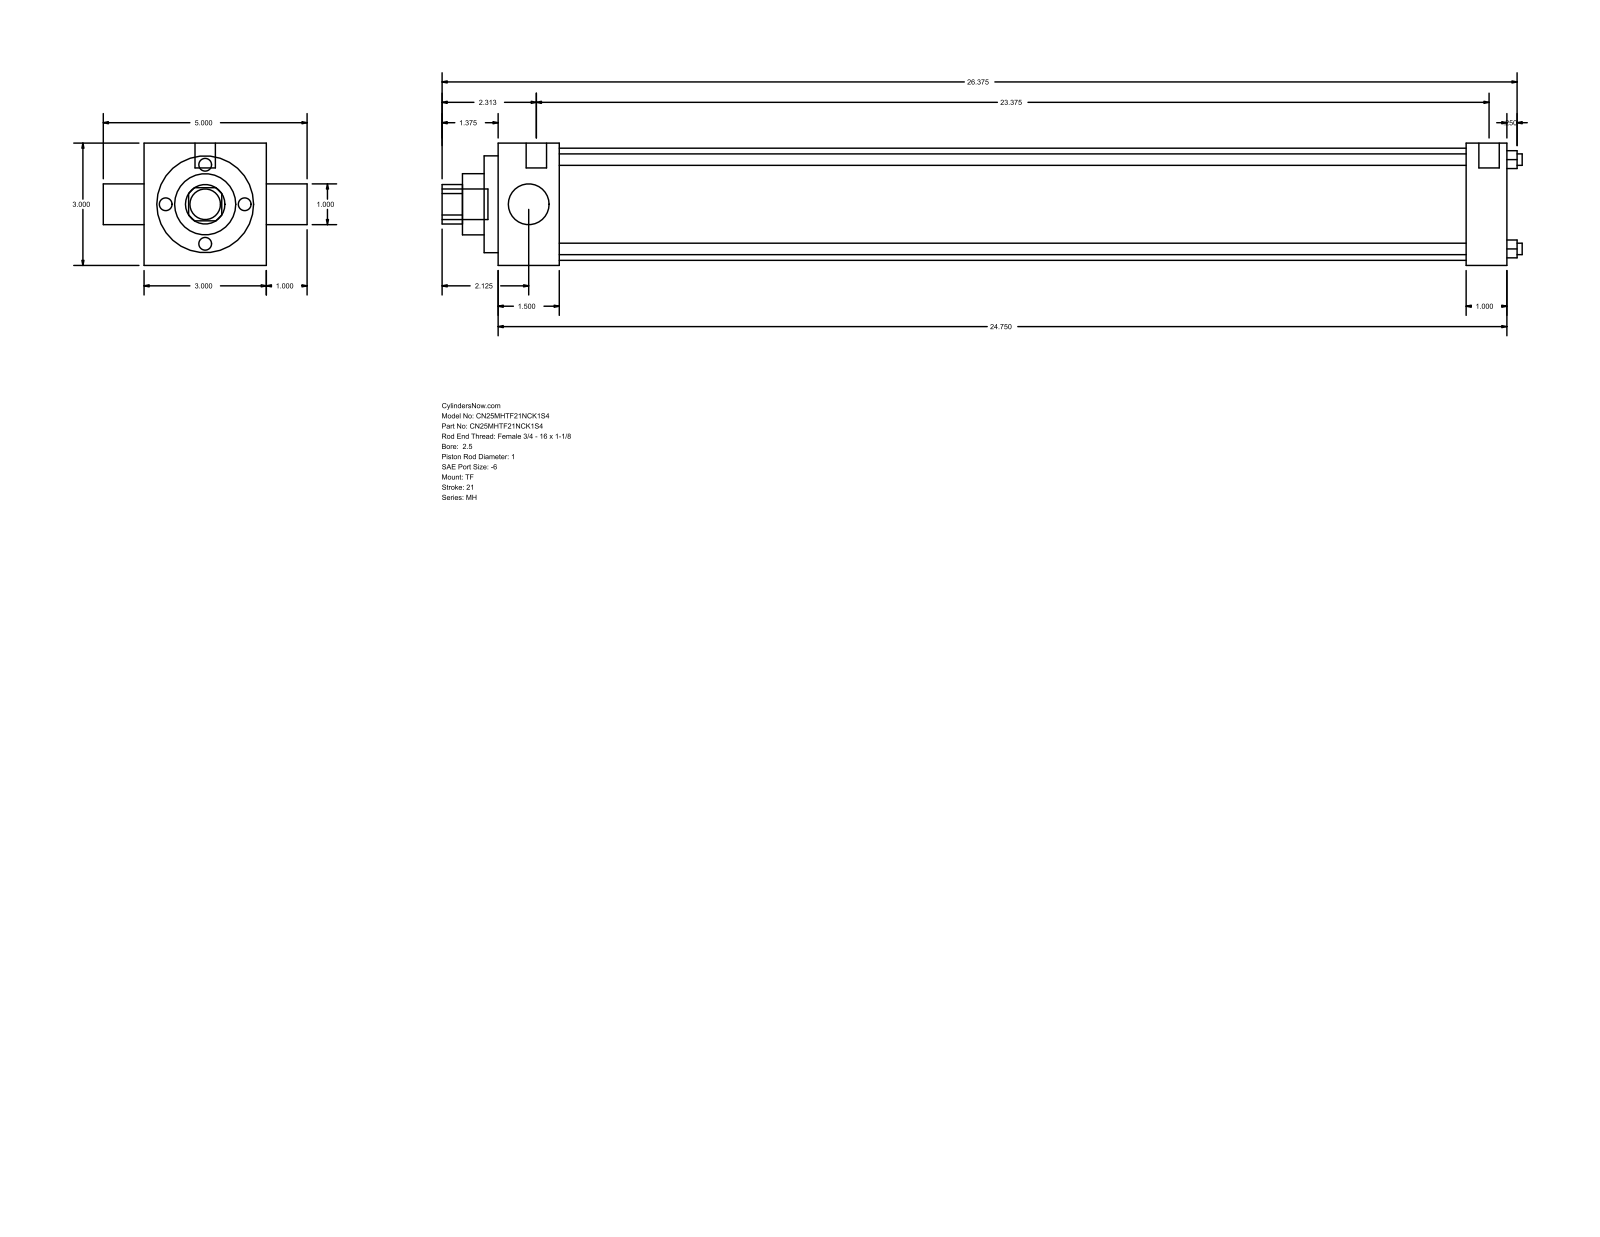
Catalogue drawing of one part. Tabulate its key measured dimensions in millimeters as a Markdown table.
| quantity | value |
| --- | --- |
| part name | MH_TF__0250_1 |
| STEP written by | GSSL Pune (CONFIG_CONTROL_DESIGN) |
| units | millimeters |
| bodies | 0 solids, 86 faces (61 planar, 25 cylindrical, 0 other) |
| overall size | 673.1 × 127 × 76.2 |
| round holes (diameter × count) | 7.14 × 4, 25.4 × 2, 38.1 × 1, 60.33 × 1, 69.85 × 1 |
| round bosses / shafts (diameter × count) | 5.56 × 3, 12.7 × 2, 19.05 × 1 |
| partial cylindrical surfaces (radius × count) | 12.29 × 1 |
| main face-to-face distances | 76.2, 628.66, 38.11, 590.55, 603.25, 565.14, 25.41, 8.73, 46.84, 611.98 |
| hole center spacings | 39.33, 55.62, 78.66 |
